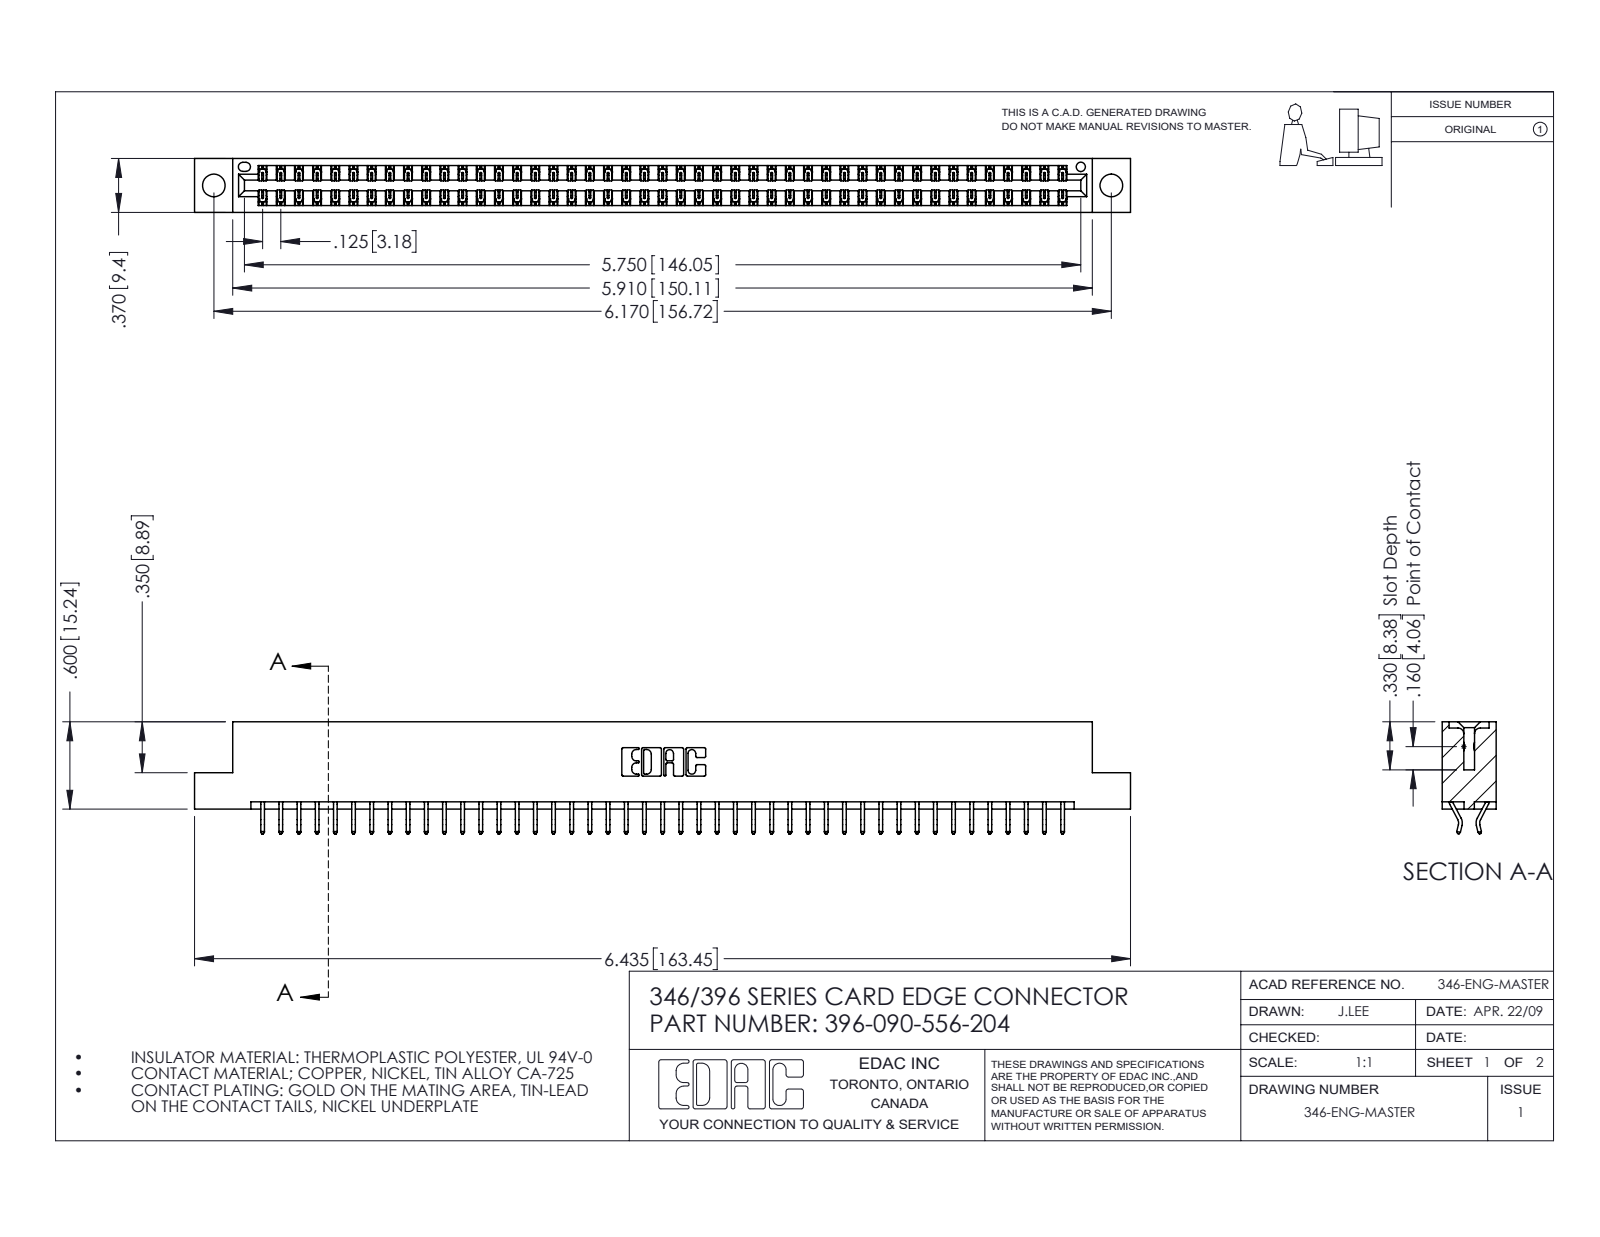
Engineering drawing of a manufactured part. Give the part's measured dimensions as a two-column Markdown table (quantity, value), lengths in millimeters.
| quantity | value |
| --- | --- |
| part name | 345-292-001_556 Tail; 346 Part_Flush Mounting Lugs - 0.156 Dia-TH; 396-090-556-204 |
| STEP written by | SolidWorks 2016 (CONFIG_CONTROL_DESIGN) |
| units | millimeters |
| bodies | 91 solids, 5342 faces (3586 planar, 1756 cylindrical, 0 other) |
| overall size | 163.4 × 19.6 × 9.4 |
| volume | 15 900 mm³ |
| surface area | 21 590 mm² |
| round holes (diameter × count) | 4 × 2, 1.6 × 1 |
| partial cylindrical surfaces (radius × count) | 0.2 × 135, 0.3 × 22, 0.2 × 6, 0.8 × 6, 0.7 × 3, 0.3 × 2, 0.4 × 2, 0.6 × 2 |
| main face-to-face distances | 1.2, 8.2, 9.4, 6.4, 0.6, 1.8, 7.6, 7, 3.8, 5.6 |
| hole center spacings | 6.2, 151.4, 156.7 |
